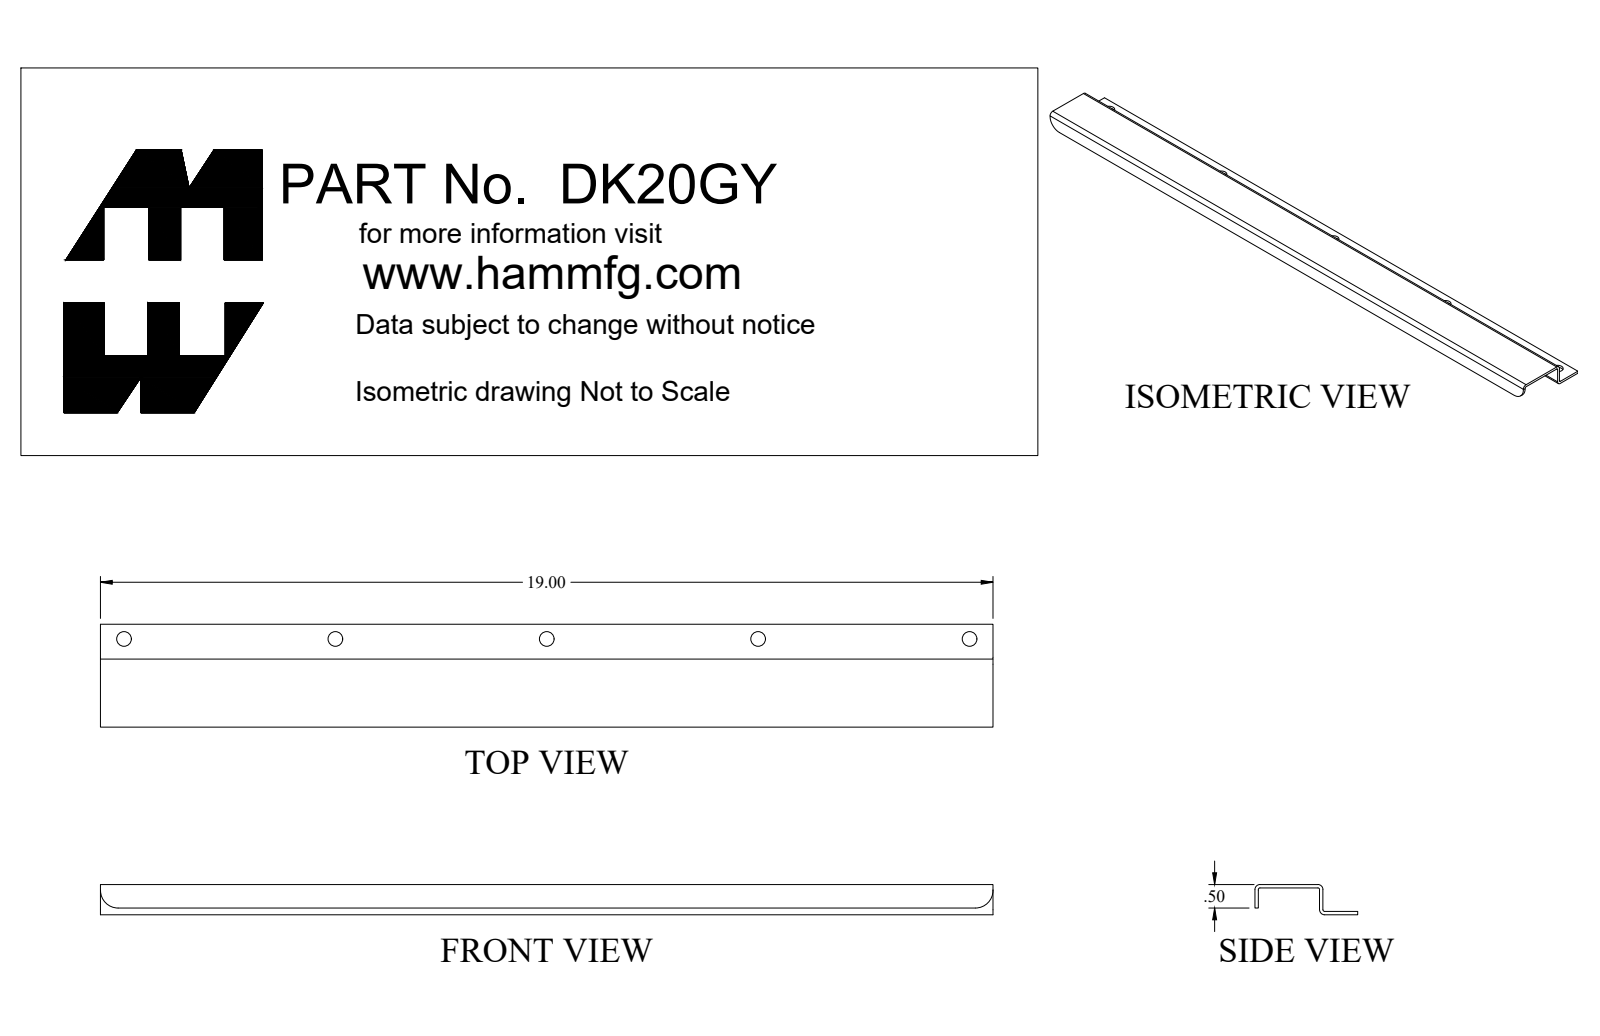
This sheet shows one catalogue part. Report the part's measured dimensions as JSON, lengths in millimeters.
{"part_name": "DK20GY_Default", "step_written_by": "SolidWorks 2018 (CONFIG_CONTROL_DESIGN)", "units": "millimeters", "bodies": {"solids": 5, "faces": 69, "planar": 35, "cylindrical": 28, "other": 6}, "overall_size": [482.6, 55.6, 33.6], "volume_mm3": 85410, "surface_area_mm2": 99290, "round_holes": [[8, 5], [5.1, 1], [7, 1]], "round_bosses_or_shafts": [[15.9, 1], [12.3, 1], [6.4, 1]], "partial_cylinders_radius": [[0.9, 3], [2.7, 3], [9.5, 2]], "face_to_face_distances": [1.8, 14.5, 16.4, 35, 12.7, 1.6, 16.1, 18, 3.4, 36.8], "hole_center_spacings": [114.3, 228.6, 342.9, 457.2]}
